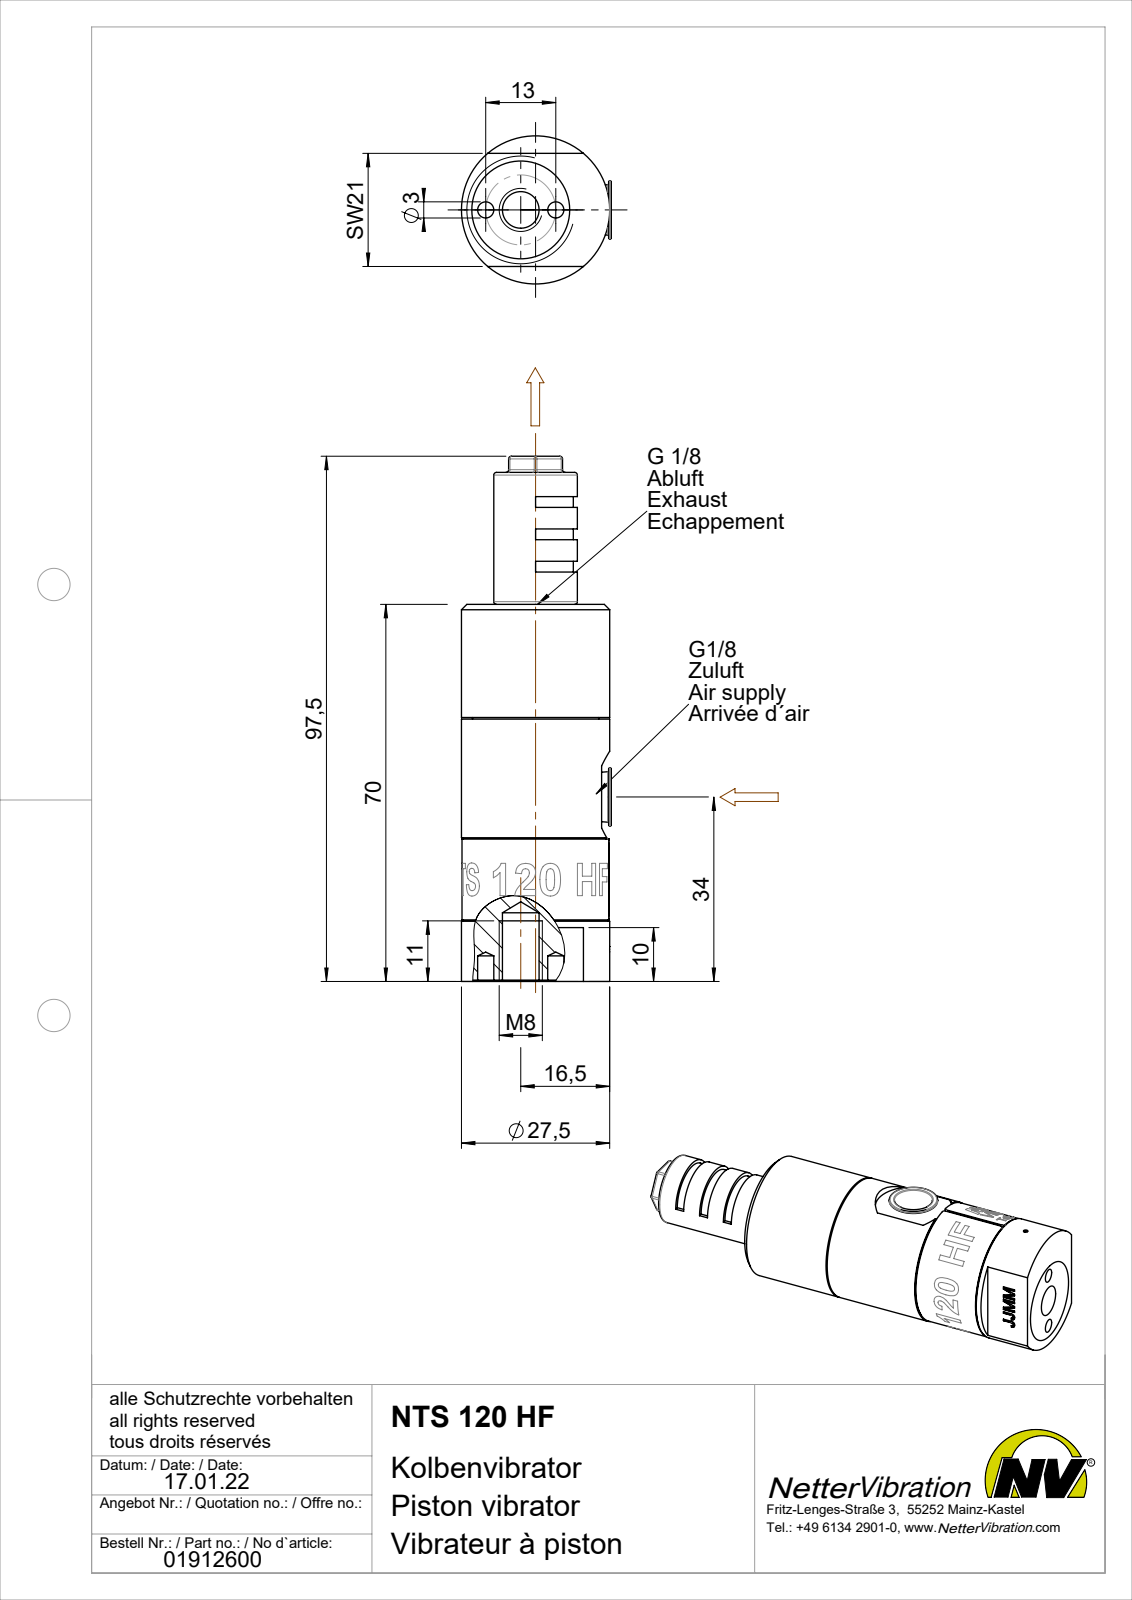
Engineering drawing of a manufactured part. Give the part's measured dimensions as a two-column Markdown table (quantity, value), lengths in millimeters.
| quantity | value |
| --- | --- |
| part name | NTS 120 HF Kolbenvibrator #01912600 |
| STEP written by | SolidWorks 2015 (AUTOMOTIVE_DESIGN) |
| units | millimeters |
| bodies | 6 solids, 316 faces (88 planar, 163 cylindrical, 65 other) |
| overall size | 97.5 × 27.5 × 27.5 |
| volume | 45 141 mm³ |
| surface area | 18 512 mm² |
| round holes (diameter × count) | 3 × 4, 1 × 2, 2.5 × 2, 1.5 × 1, 6.8 × 1, 8.57 × 1, 8.8 × 1, 8.9 × 1, 10.5 × 1, 13 × 1, 18.16 × 1, 22 × 1 |
| round bosses / shafts (diameter × count) | 27.5 × 1, 27.3 × 1, 23.4 × 1, 23 × 1, 21.5 × 1, 20 × 1, 15.5 × 1, 9.73 × 1 |
| partial cylindrical surfaces (radius × count) | 0.5 × 22, 7 × 1, 8.5 × 1 |
| main face-to-face distances | 12, 45, 13, 11.7, 21, 9.3, 69.75, 58.05, 57.75, 57 |
| hole center spacings | 6.5, 6.53, 7.82, 8.61, 9.63, 10, 13, 15.07 |
